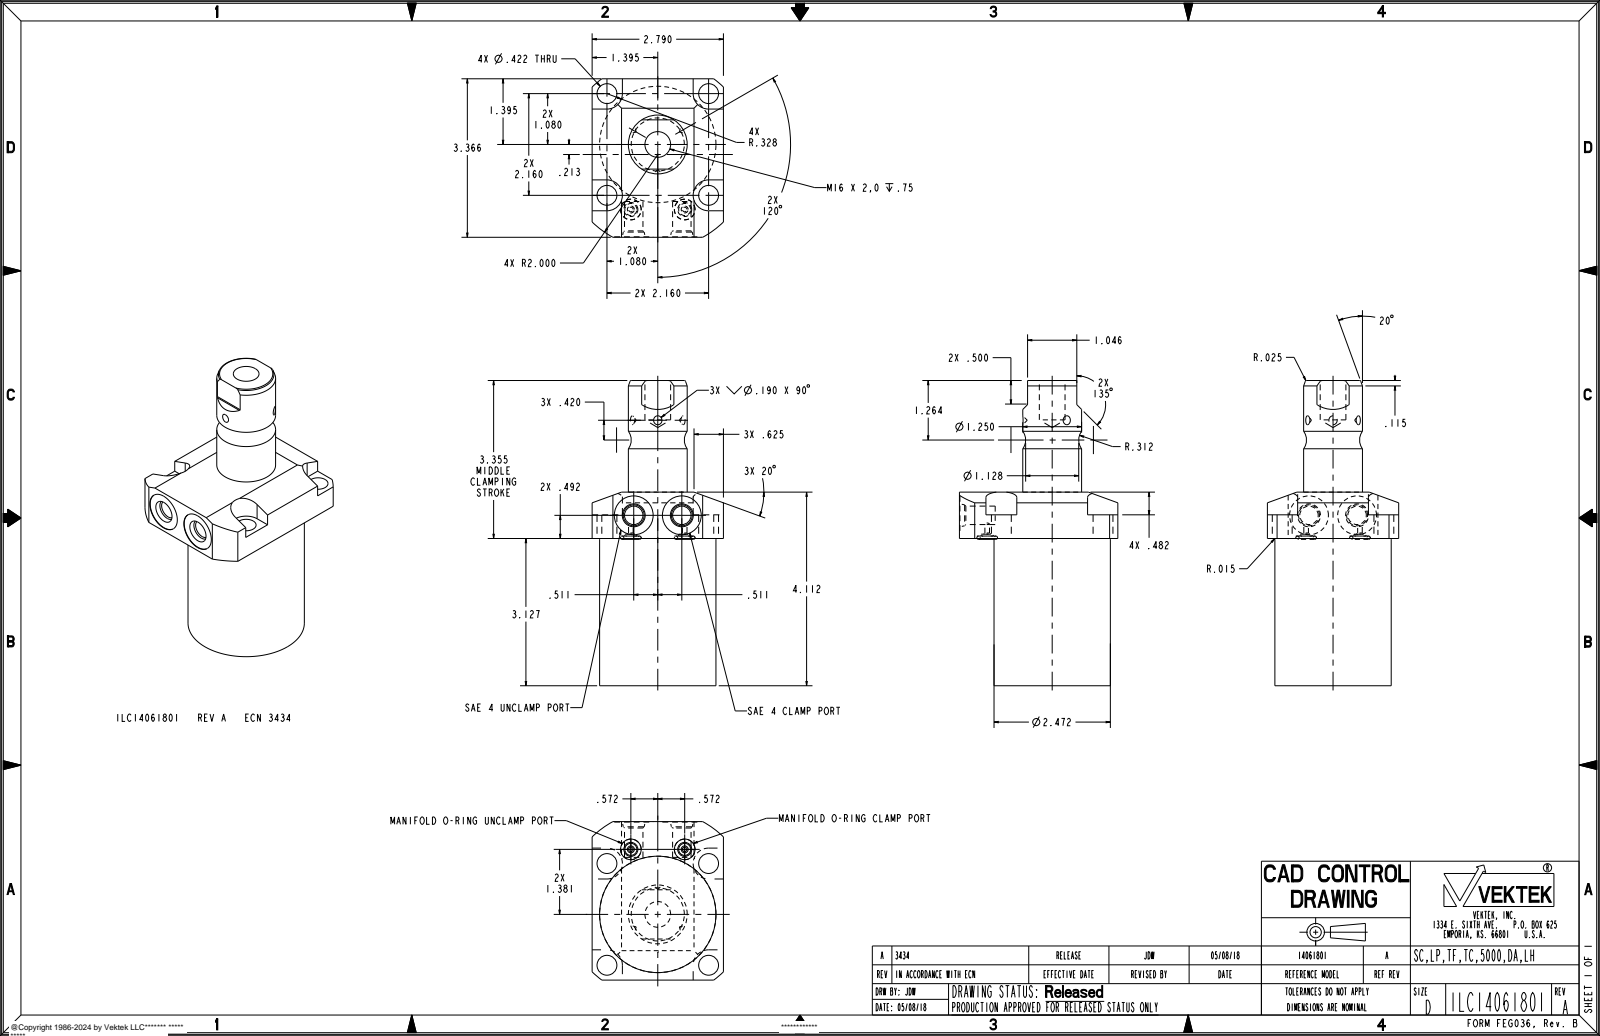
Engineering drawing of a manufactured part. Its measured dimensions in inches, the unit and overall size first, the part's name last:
Units: inches
Overall size (bounding box): 6.482 × 3.366 × 2.79
Round holes (diameter × count): ⌀0.422 ×4, ⌀0.098 ×2, ⌀0.256 ×2, ⌀0.392 ×2, ⌀0.438 ×2, ⌀0.825 ×2, ⌀0.546 ×1
Round bosses / shafts (diameter × count): ⌀2.472 ×1, ⌀1.25 ×1
Partial cylindrical surfaces — rounded edges, fillets, slot ends (radius × count): R0.328 ×4, R0.03 ×2, R2 ×1
Main face-to-face distances: 3.127, 4.112, 0.985, 2.79, 3.63, 0.503, 0.482, 3.366, 6.482, 3.355
Hole centre spacings: 1.527, 2.16, 0.591, 1.495, 1.679, 2.513, 2.964, 3.054
Volume: 25.08 in³ · Surface area: 68.26 in²
Bodies: 3 solids, 119 faces (37 planar, 46 cylindrical, 36 other)
Part name (STEP PRODUCT): ILC14061801
STEP written by: PRO/ENGINEER BY PARAMETRIC TECHNOLOGY CORPORATION, 2013320 (AUTOMOTIVE_DESIGN)
